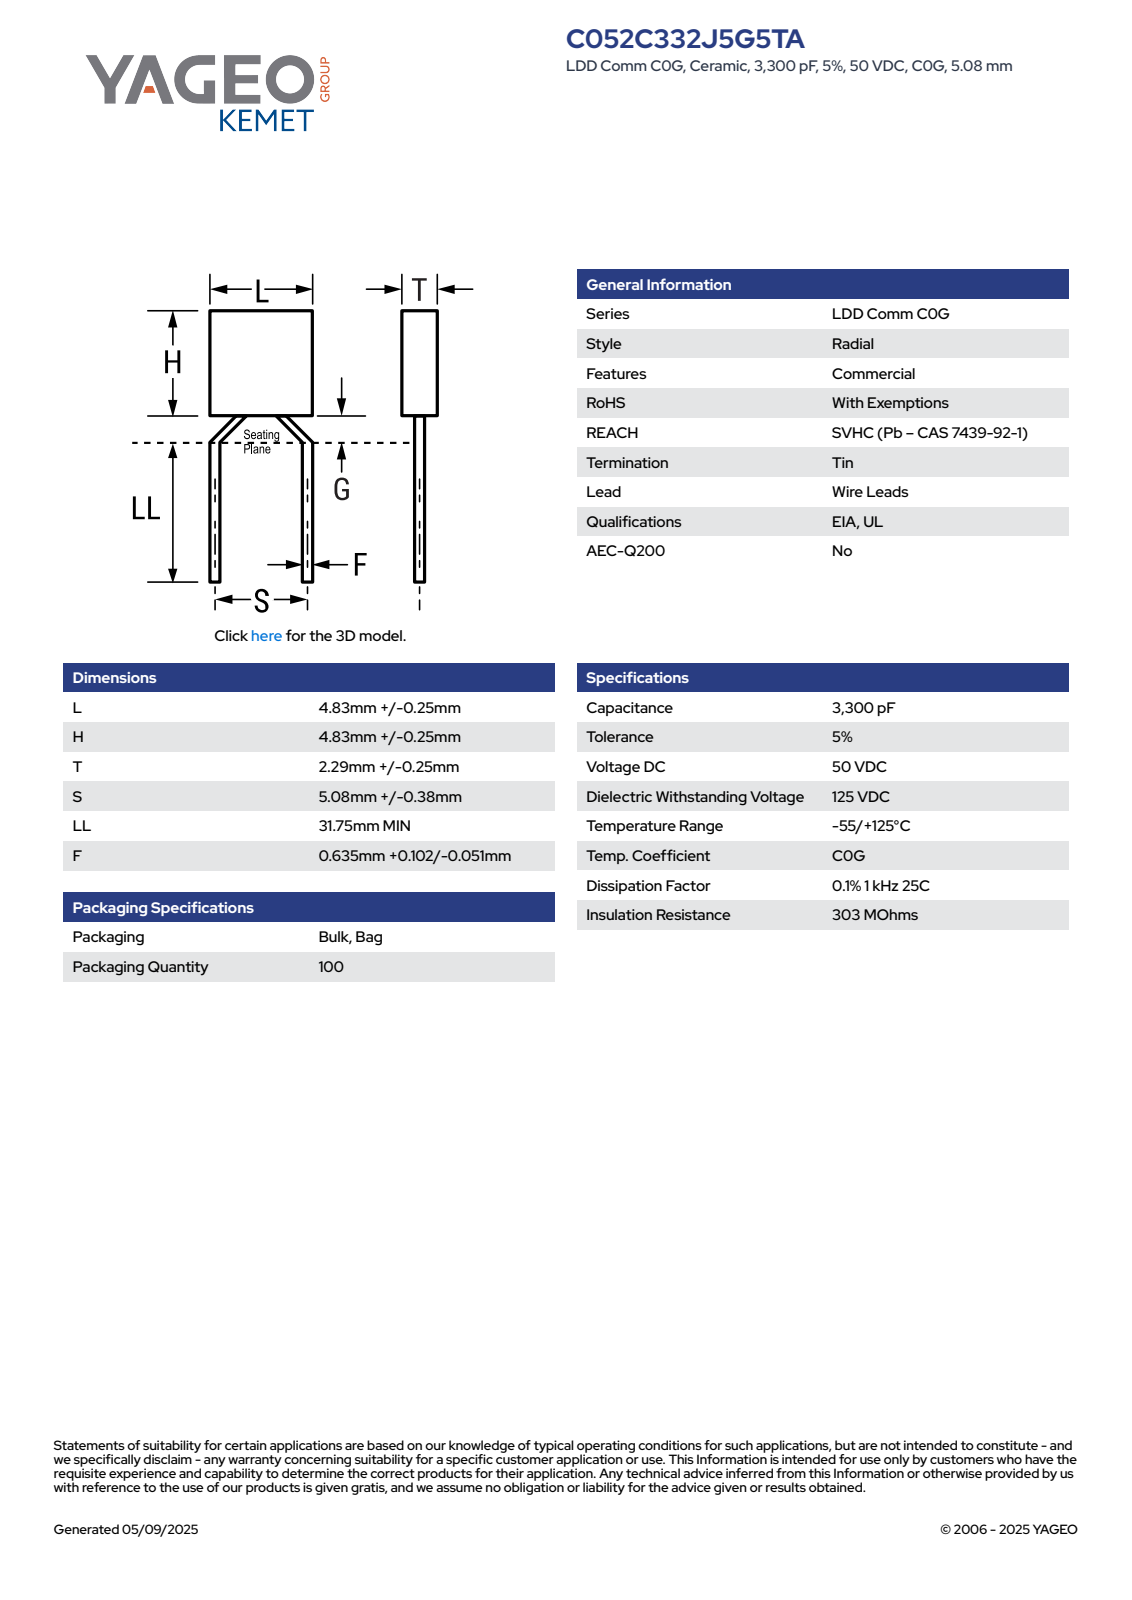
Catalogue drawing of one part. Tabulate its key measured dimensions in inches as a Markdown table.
| quantity | value |
| --- | --- |
| part name | CCR_RMST_C052_L5.08H5.08T2.54S5.46LL31.75F0.735 |
| STEP written by | SolidWorks 2014 (AUTOMOTIVE_DESIGN) |
| units | inches |
| bodies | 4 solids, 73 faces (65 planar, 4 cylindrical, 4 other) |
| overall size | 1.45 × 0.244 × 0.1 |
| volume | 0.006 in³ |
| surface area | 0.395 in² |
| round bosses / shafts (diameter × count) | 0.029 × 2 |
| main face-to-face distances | 0.1, 0.2, 1.25, 1.45, 0.036, 0.082, 1.368, 0.118, 0.082, 1.332 |
